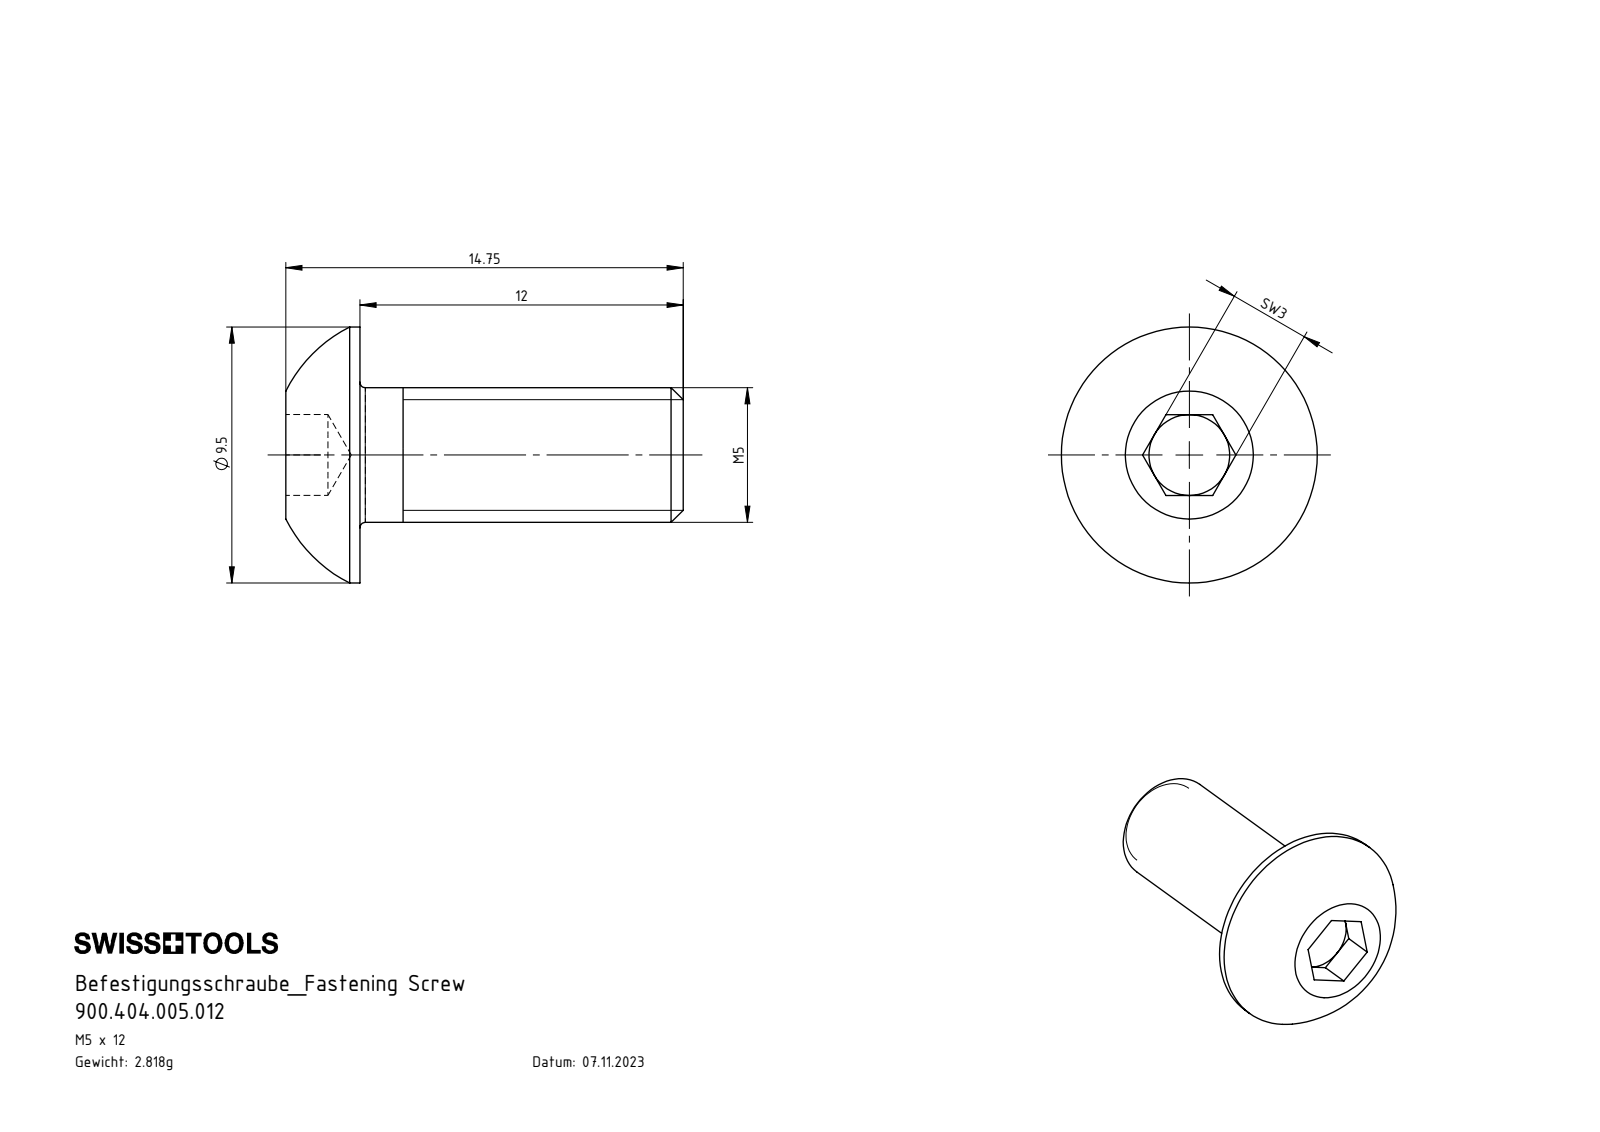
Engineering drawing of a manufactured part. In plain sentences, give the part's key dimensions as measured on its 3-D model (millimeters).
The part is named "900.404.005.012". Its 3-D file was written by "SolidWorks 2022 (AUTOMOTIVE_DESIGN)". It is 1 solid with 27 faces: 15 planar, 4 cylindrical and 8 other. Overall it measures 14.75 by 9.5 by 9.5 millimeters. Its volume is 359 cubic millimeters and its surface area 379 square millimeters. Round bosses or shafts: 1 of diameter 9.5, 1 of diameter 5. The main face-to-face distances are 12, 2.75, 14.75, 3, 1.56, 1.19, 13.19.
